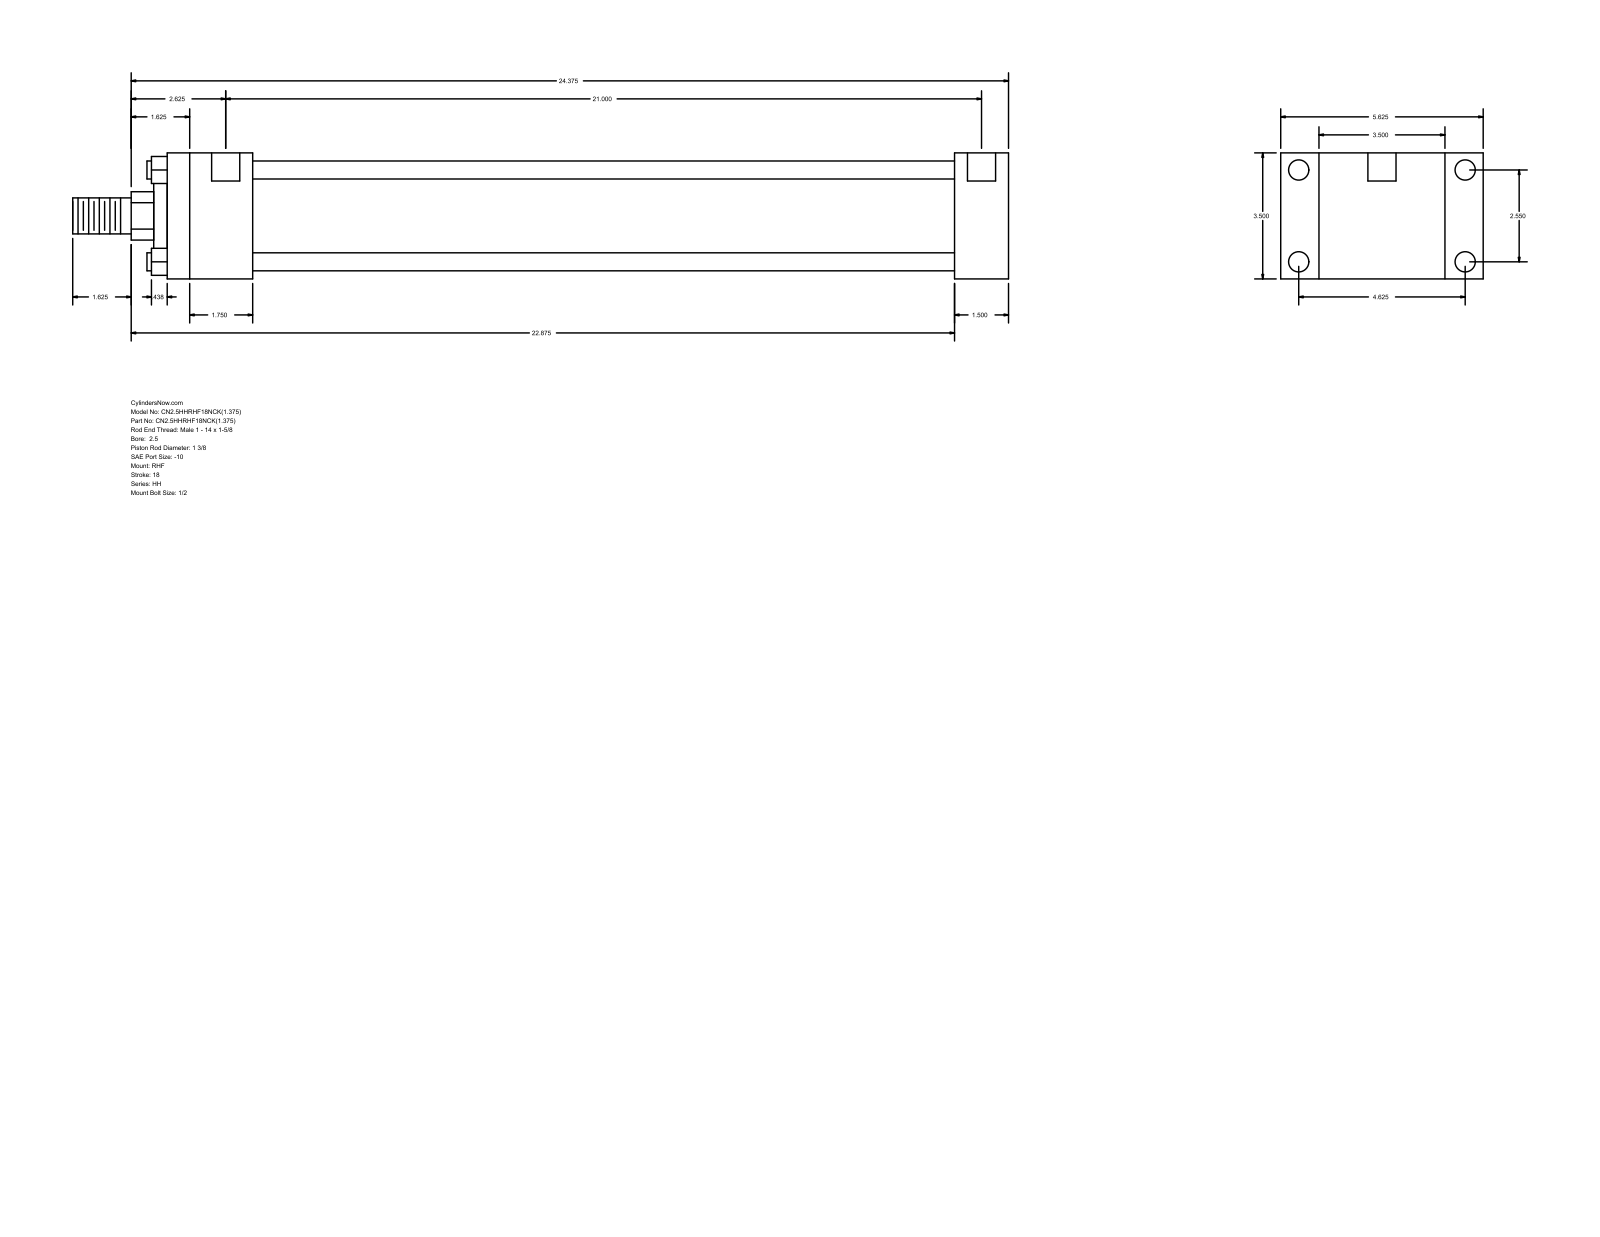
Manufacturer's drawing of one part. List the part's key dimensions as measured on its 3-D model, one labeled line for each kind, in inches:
Part name (STEP PRODUCT): HH_RHF__0250_1.375
STEP written by: GSSL Pune (CONFIG_CONTROL_DESIGN)
Units: inches
Bodies: 0 solids, 88 faces (60 planar, 28 cylindrical, 0 other)
Overall size (bounding box): 26 × 5.625 × 3.5
Round holes (diameter × count): ⌀0.219 ×4, ⌀0.563 ×4, ⌀0.781 ×2
Round bosses / shafts (diameter × count): ⌀0.5 ×4, ⌀2.875 ×1, ⌀2 ×1, ⌀1.375 ×1, ⌀1 ×1
Partial cylindrical surfaces — rounded edges, fillets, slot ends (radius × count): R0.672 ×1
Main face-to-face distances: 3.5, 1.5, 1.063, 4.563, 21.875, 23.375, 5.625, 2.375, 19.5, 21
Hole centre spacings: 0.062, 2.55, 4.625, 5.281, 21.063, 21.125, 21
